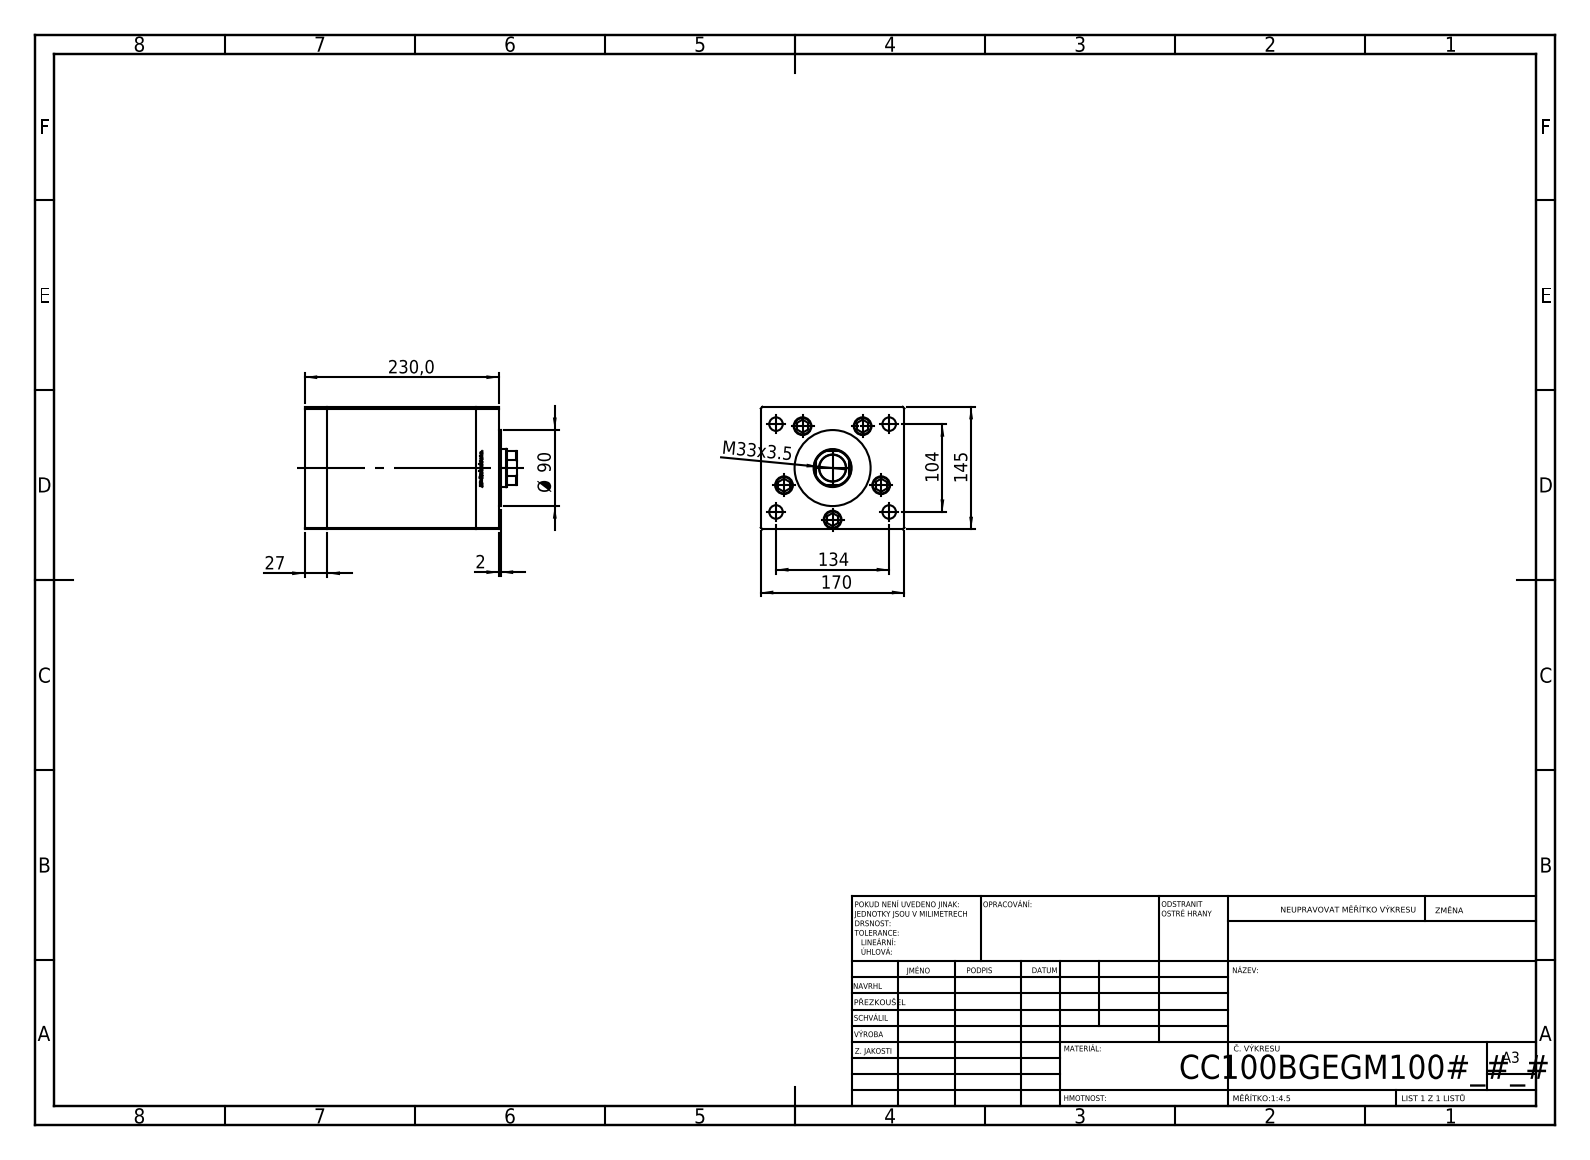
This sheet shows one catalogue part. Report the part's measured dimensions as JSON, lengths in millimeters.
{"part_name": "V220C_B MIDDLE; V220C BACK_B; V220C_FRONT_B; ALLEN BOLT (+1 more)", "step_written_by": "SolidWorks 2019 (CONFIG_CONTROL_DESIGN)", "units": "millimeters", "bodies": {"solids": 14, "faces": 1185, "planar": 464, "cylindrical": 147, "other": 574}, "overall_size": [251, 170, 145], "volume_mm3": 4878000, "surface_area_mm2": 455142, "round_holes": [[17.5, 5], [21, 5], [16, 4], [2, 2], [13.16, 2], [31.5, 1], [45, 1]], "round_bosses_or_shafts": [[8, 5], [100, 1], [90, 1]], "partial_cylinders_radius": [[0.93, 2], [22, 1]], "face_to_face_distances": [27, 203, 176, 145, 170, 38, 11, 230, 165, 192], "hole_center_spacings": [61, 84.81, 31.53, 33.06, 67.6, 70.44, 72.95, 73.26]}
